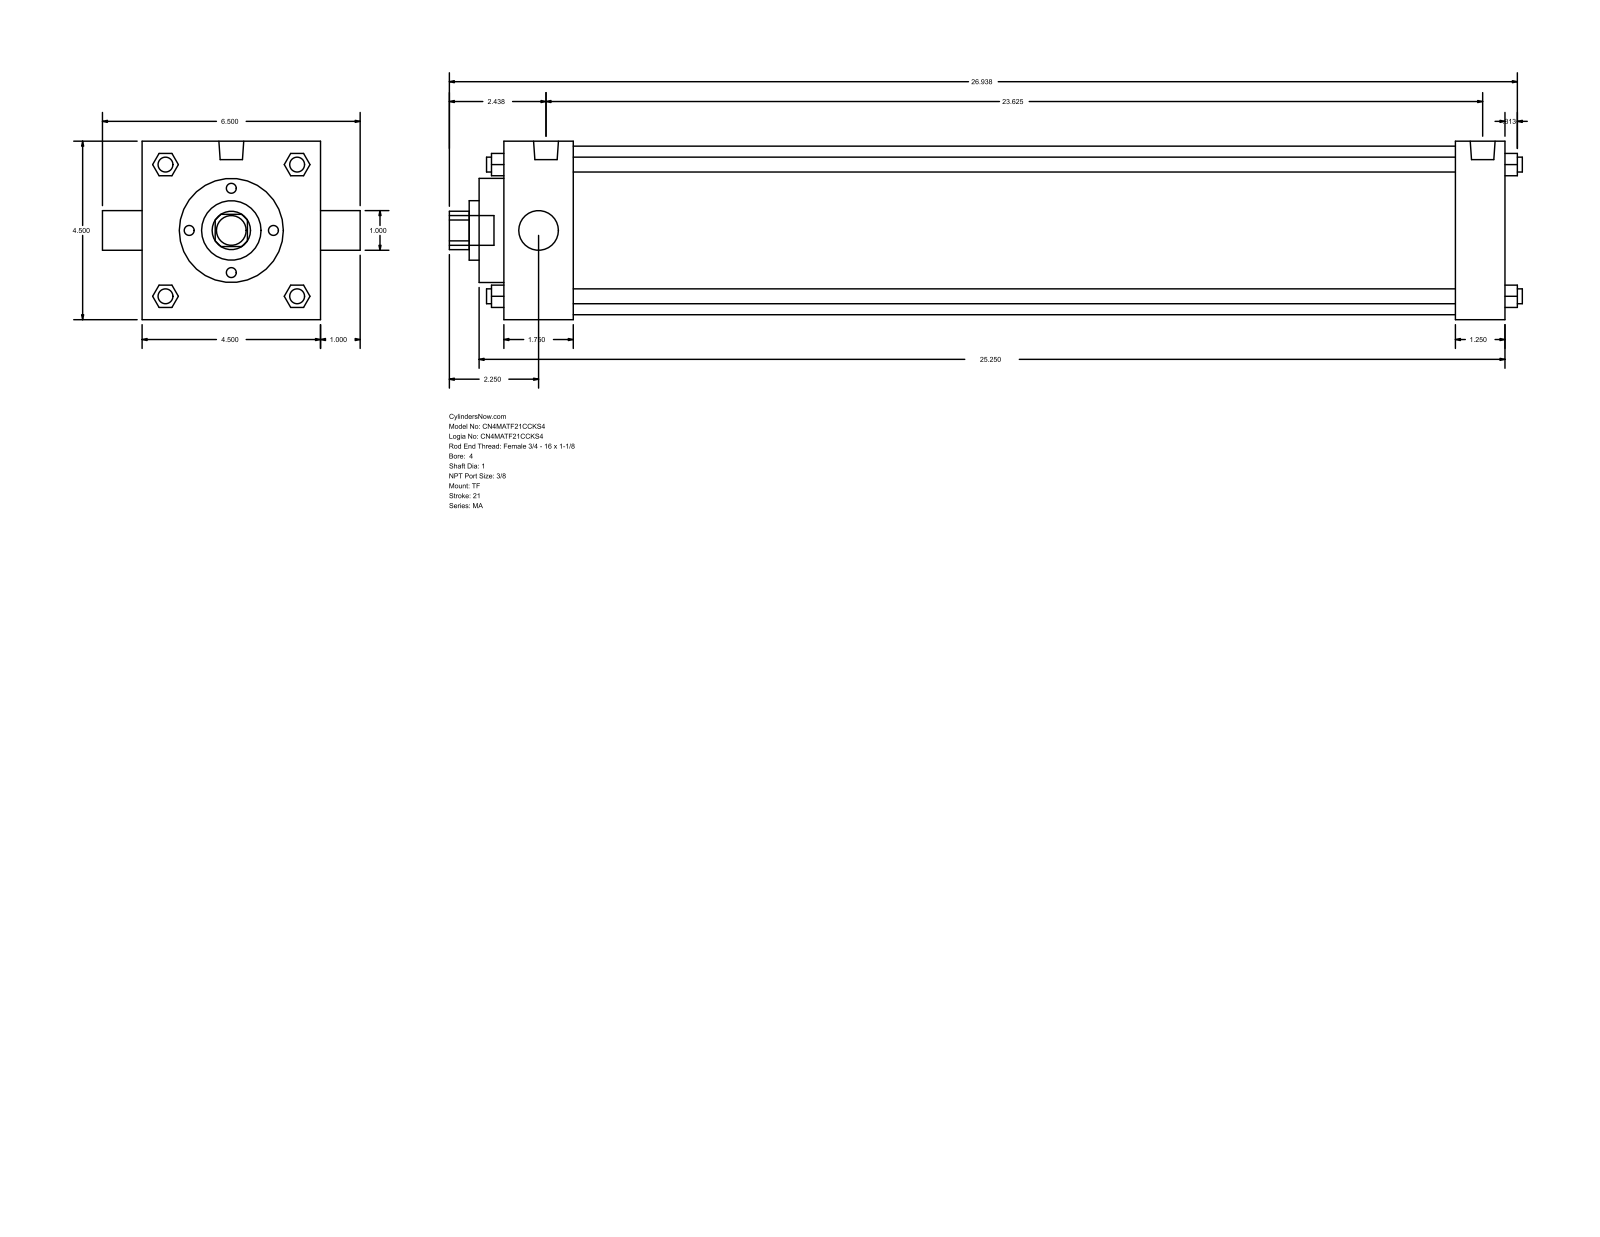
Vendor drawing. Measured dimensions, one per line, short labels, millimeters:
name: MA_TF__0400_1
written by: GSSL Pune (CONFIG_CONTROL_DESIGN)
unit: mm
bodies: 0 solids, 122 faces (93 planar, 29 cylindrical, 0 other)
size: 687.39 × 165.1 × 114.3
holes: 2× ⌀25.4, 1× ⌀38.1, 1× ⌀66.67, 1× ⌀107.95
bosses: 4× ⌀9.53, 3× ⌀11.11, 2× ⌀15.93, 1× ⌀19.05
rounds: 1× R12.29
face distances: 114.3, 641.35, 609.6, 31.75, 44.46, 565.14, 596.89, 657.22, 15.87, 60.33
